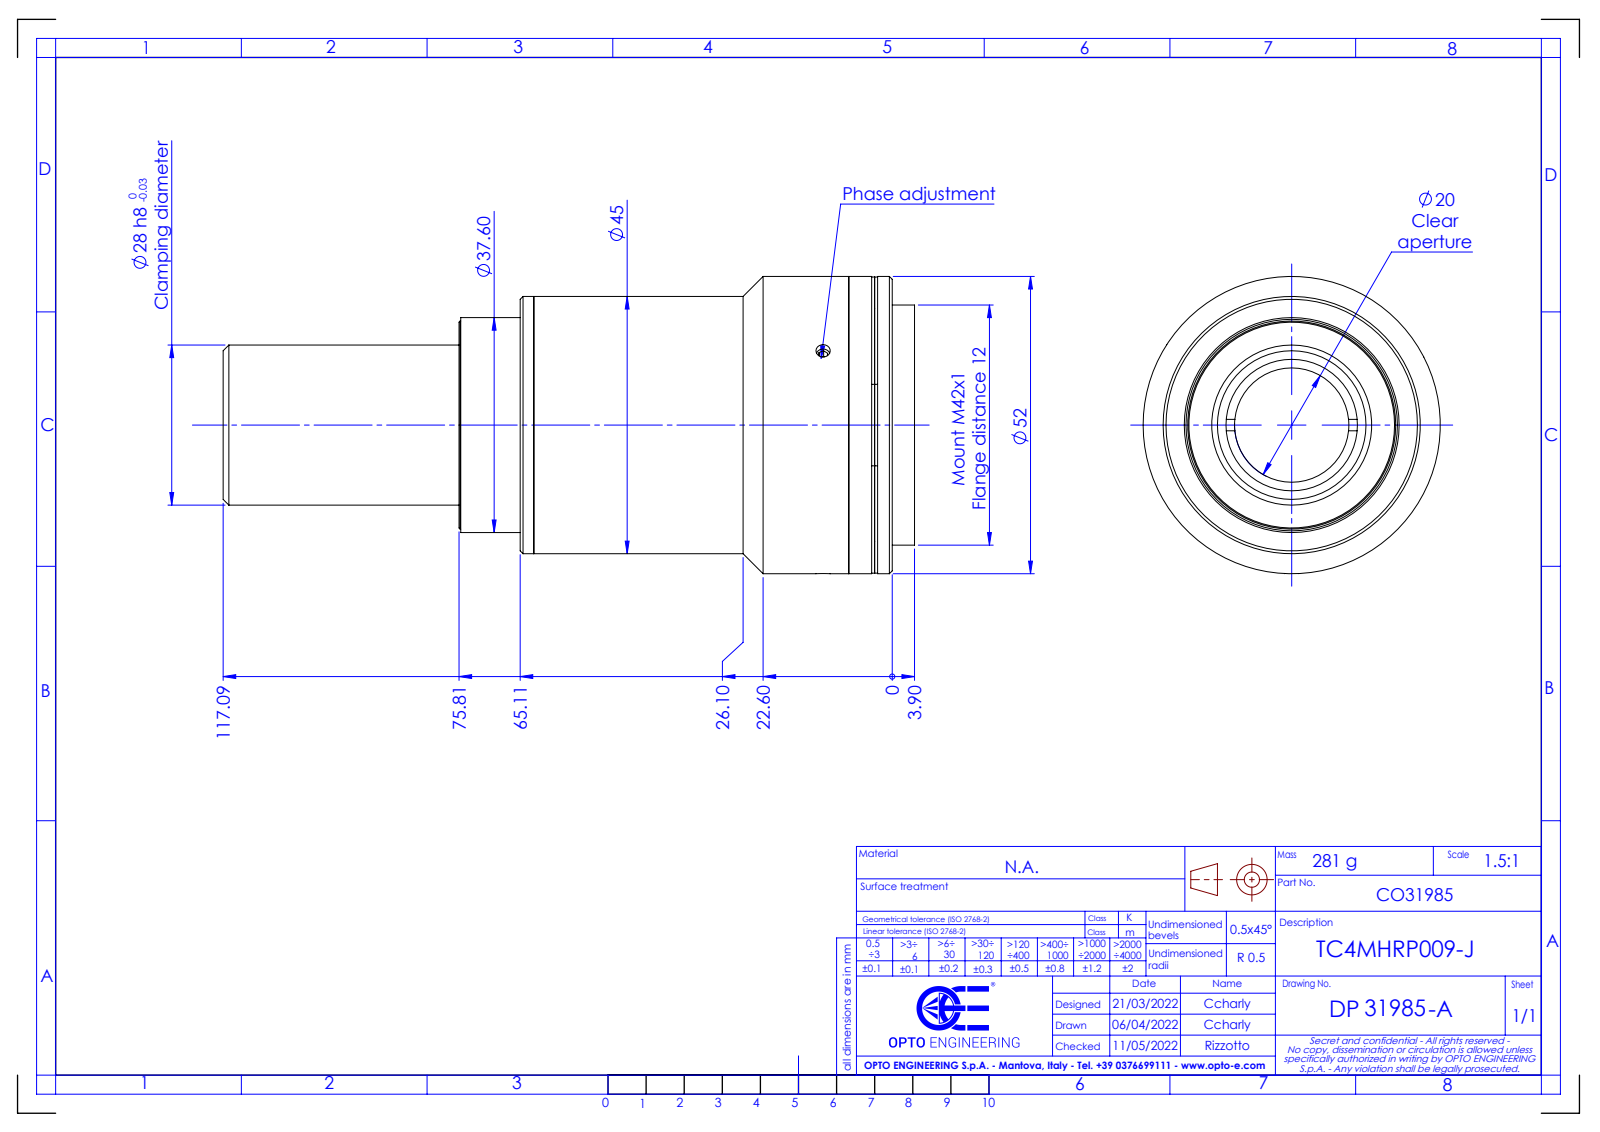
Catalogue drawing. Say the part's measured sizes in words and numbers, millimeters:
The part is named "DP31985-A_TC4MHRP009-J". Its 3-D file was written by "SolidWorks 2021 (CONFIG_CONTROL_DESIGN)". It is 0 solids with 95 faces: 37 planar, 36 cylindrical and 22 other. Overall it measures 120.99 by 52 by 52 millimeters. Round holes: 3 of diameter 2.5, 1 of diameter 20, 1 of diameter 23, 1 of diameter 38, 1 of diameter 41. Round bosses or shafts: 1 of diameter 52, 1 of diameter 51.8, 1 of diameter 45, 1 of diameter 42, 1 of diameter 37.6, 1 of diameter 36.4, 1 of diameter 28. The main face-to-face distances are 0.5, 0.54, 5.04, 4, 1.04, 7.6, 3.6, 2.56, 4.5, 3.1.
